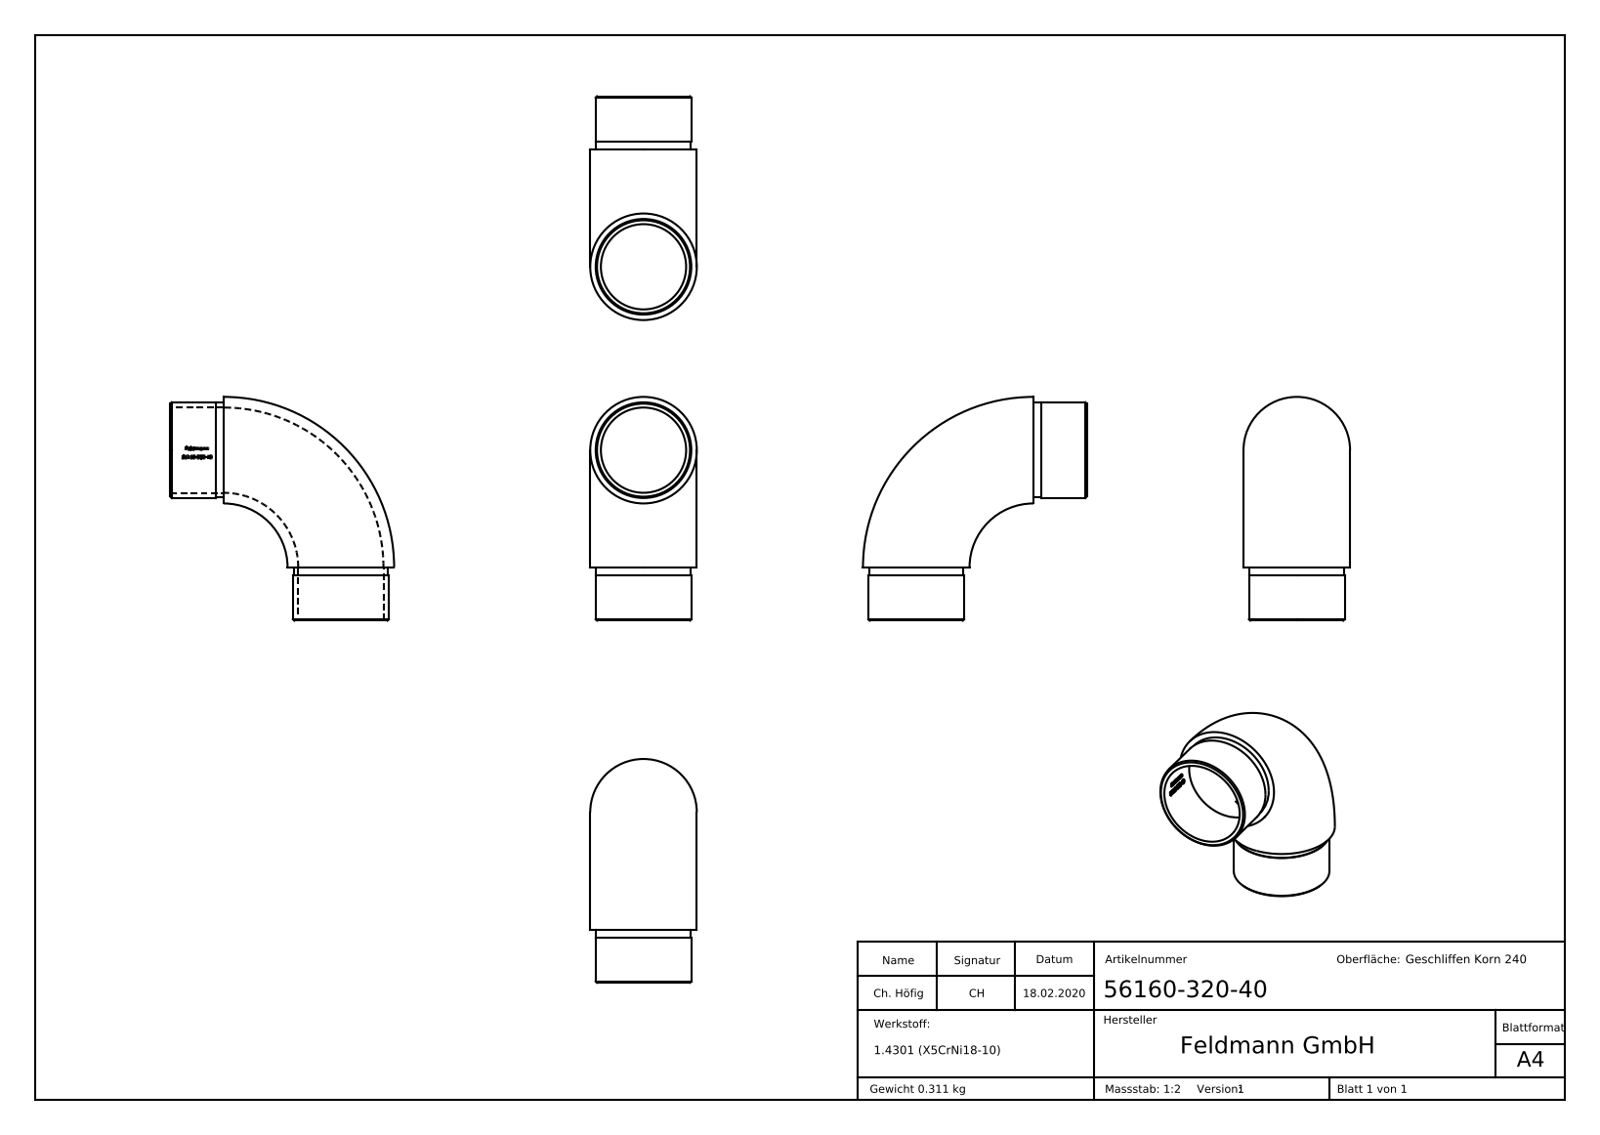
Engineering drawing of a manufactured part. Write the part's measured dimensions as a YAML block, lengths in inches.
part_name: "56160-320-40"
step_written_by: "SolidWorks 2015 (CONFIG_CONTROL_DESIGN)"
units: inches
bodies: {solids: 1, faces: 268, planar: 108, cylindrical: 35, other: 125}
overall_size: [3.307, 3.307, 1.575]
volume: 2.406
surface_area: 38.9
round_holes:
  - {diameter: 1.26, count: 2}
round_bosses_or_shafts:
  - {diameter: 1.413, count: 2}
  - {diameter: 1.398, count: 2}
partial_cylinders:
  - {radius: 0.634, count: 1}
face_to_face_distances: [0.787, 0.669, 0.118, 0.015, 0.047, 0.117, 0.144, 0.129, 0.037, 0.042]
